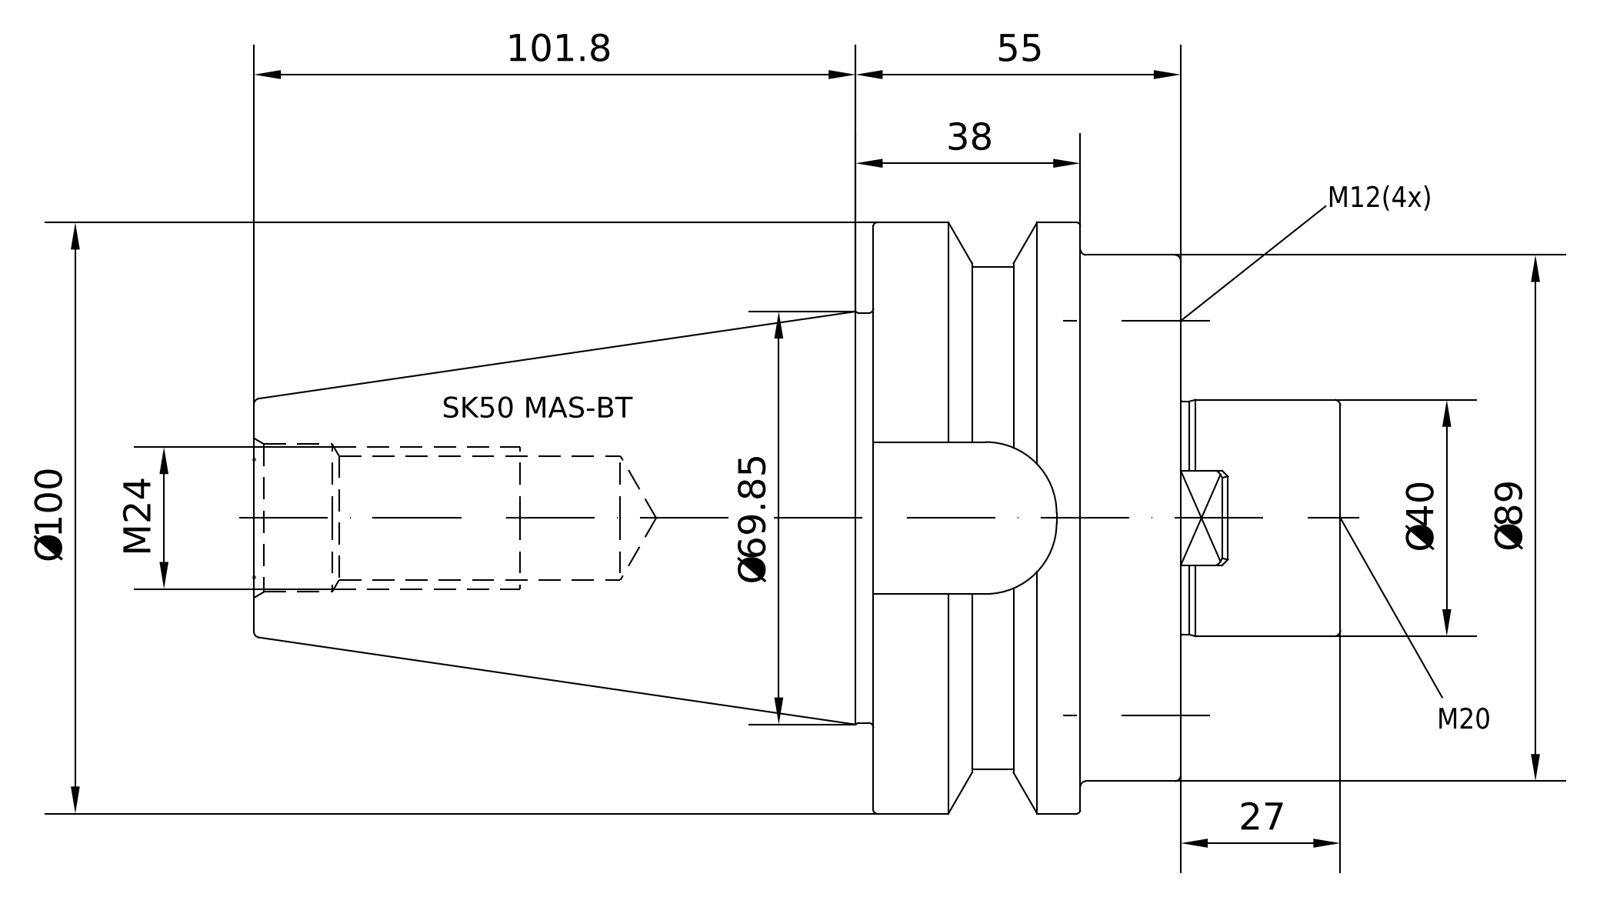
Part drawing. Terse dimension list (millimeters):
name: 50-550-40
written by: PRO/ENGINEER BY PARAMETRIC TECHNOLOGY CORPORATION, 2010430 (CONFIG_CONTROL_DESIGN)
unit: mm
bodies: 1 solid, 141 faces (41 planar, 42 cylindrical, 58 other)
size: 183.8 × 99.97 × 99.97
volume: 592 055 mm³; area: 71 848 mm²
holes: 4× ⌀10.2, 4× ⌀12, 1× ⌀17.5, 1× ⌀20, 1× ⌀20.75, 1× ⌀25.02, 1× ⌀25.7
bosses: 1× ⌀99.97, 1× ⌀89, 1× ⌀84.75, 1× ⌀69.15, 1× ⌀40, 1× ⌀24.01
rounds: 1× R12.9
face distances: 52, 35, 17, 79, 44, 27, 70.4, 60, 25, 8
hole spacings: 33.35, 47.16, 66.69
